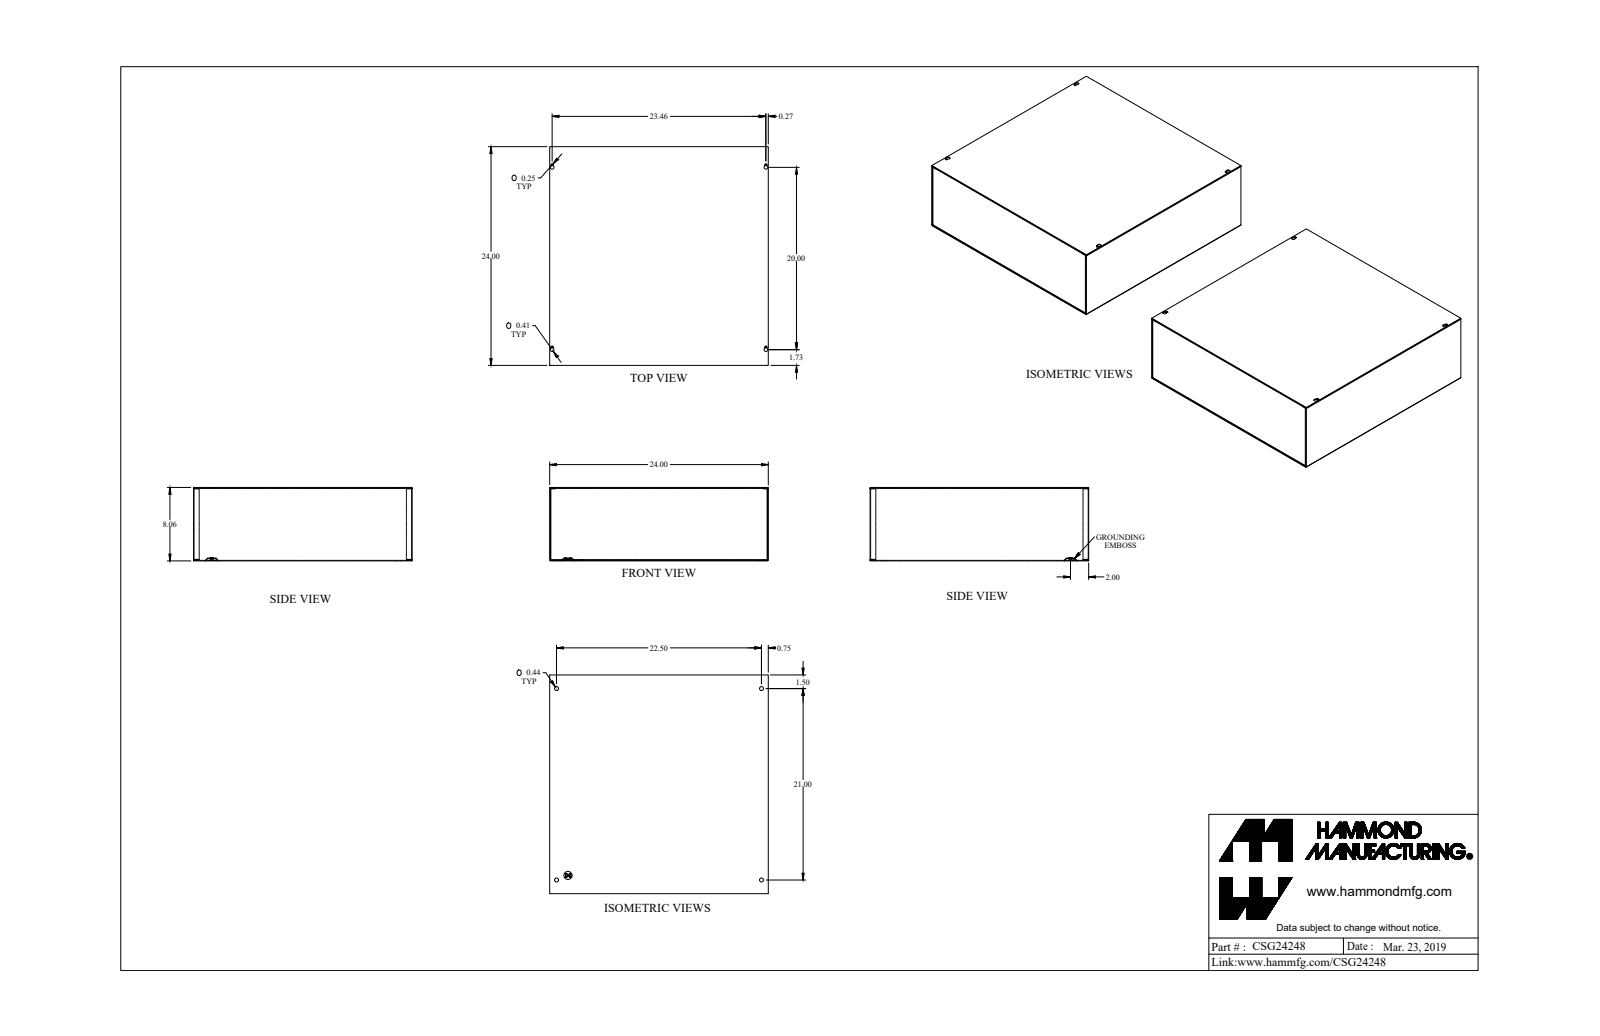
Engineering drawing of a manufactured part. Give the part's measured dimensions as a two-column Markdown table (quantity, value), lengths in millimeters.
| quantity | value |
| --- | --- |
| part name | CSG24248_Default |
| STEP written by | SolidWorks 2019 (CONFIG_CONTROL_DESIGN) |
| units | millimeters |
| bodies | 4 solids, 205 faces (125 planar, 72 cylindrical, 8 other) |
| overall size | 609.6 × 609.6 × 204.6 |
| volume | 1 860 000 mm³ |
| surface area | 2 583 000 mm² |
| round holes (diameter × count) | 4.3 × 5, 11.1 × 4, 12.7 × 1 |
| round bosses / shafts (diameter × count) | 12.5 × 1, 7.2 × 1 |
| partial cylindrical surfaces (radius × count) | 0.7 × 12, 2.2 × 12, 1.4 × 8, 3.2 × 4, 5.2 × 4 |
| main face-to-face distances | 1.4, 203.2, 608.2, 201.8, 204.6, 609.6, 606.7, 2, 199.7, 201.2 |
| hole center spacings | 17.6, 520.9, 583.8, 782.2, 508, 533.4, 571.5, 595.9 |
